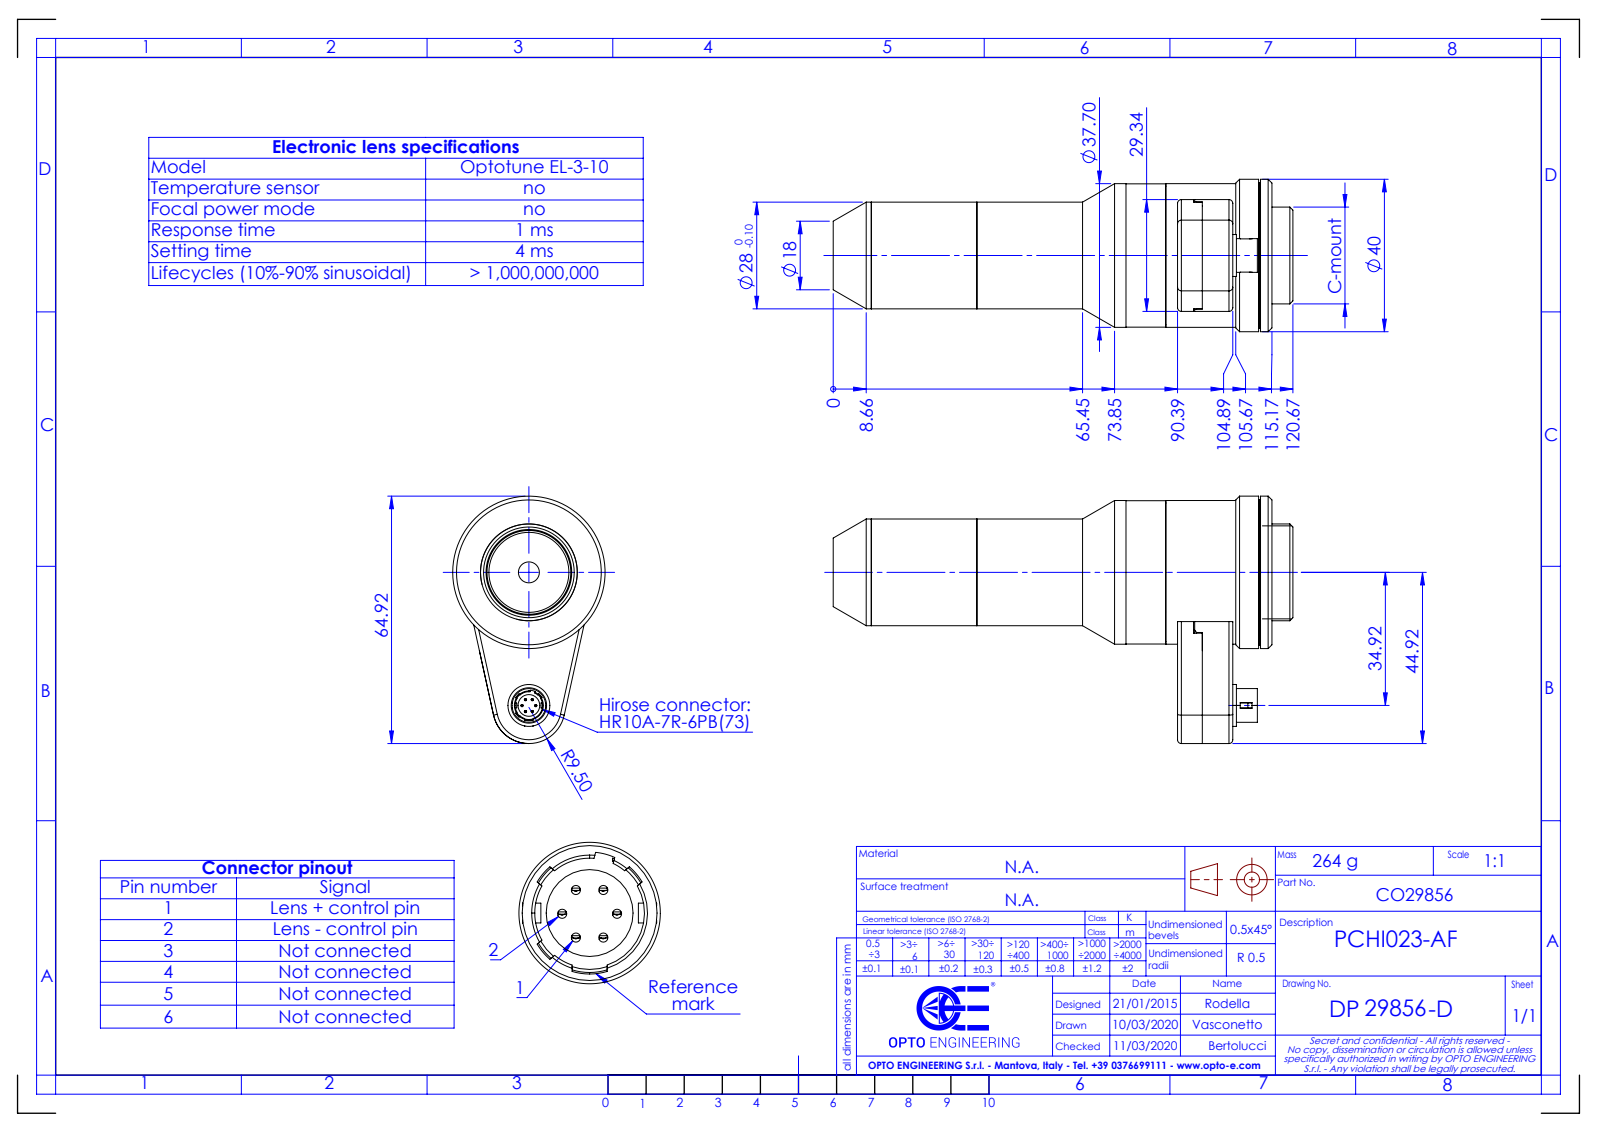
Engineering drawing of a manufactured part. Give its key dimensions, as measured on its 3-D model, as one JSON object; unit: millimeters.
{"part_name": "DP29856-D_PCHI023-AF", "step_written_by": "SolidWorks 2021 (CONFIG_CONTROL_DESIGN)", "units": "millimeters", "bodies": {"solids": 0, "faces": 191, "planar": 61, "cylindrical": 92, "other": 38}, "overall_size": [120.67, 64.92, 40], "round_holes": [[4.7, 2], [0.5, 1], [5.5, 1], [7.4, 1], [22.5, 1]], "round_bosses_or_shafts": [[1.2, 2], [40, 1], [37.7, 1], [37.6, 1], [28, 1], [25.4, 1], [11, 1], [8.85, 1]], "partial_cylinders_radius": [[0.31, 10], [0.17, 8], [1, 4], [0.4, 2], [0.92, 2], [3.6, 1], [3.9, 1], [4, 1]], "face_to_face_distances": [0.5, 3.5, 3, 24.32, 24.82, 27.82, 77.35, 101.67, 102.17, 105.17], "hole_center_spacings": [10.27, 27.03, 11.5, 34.92]}
